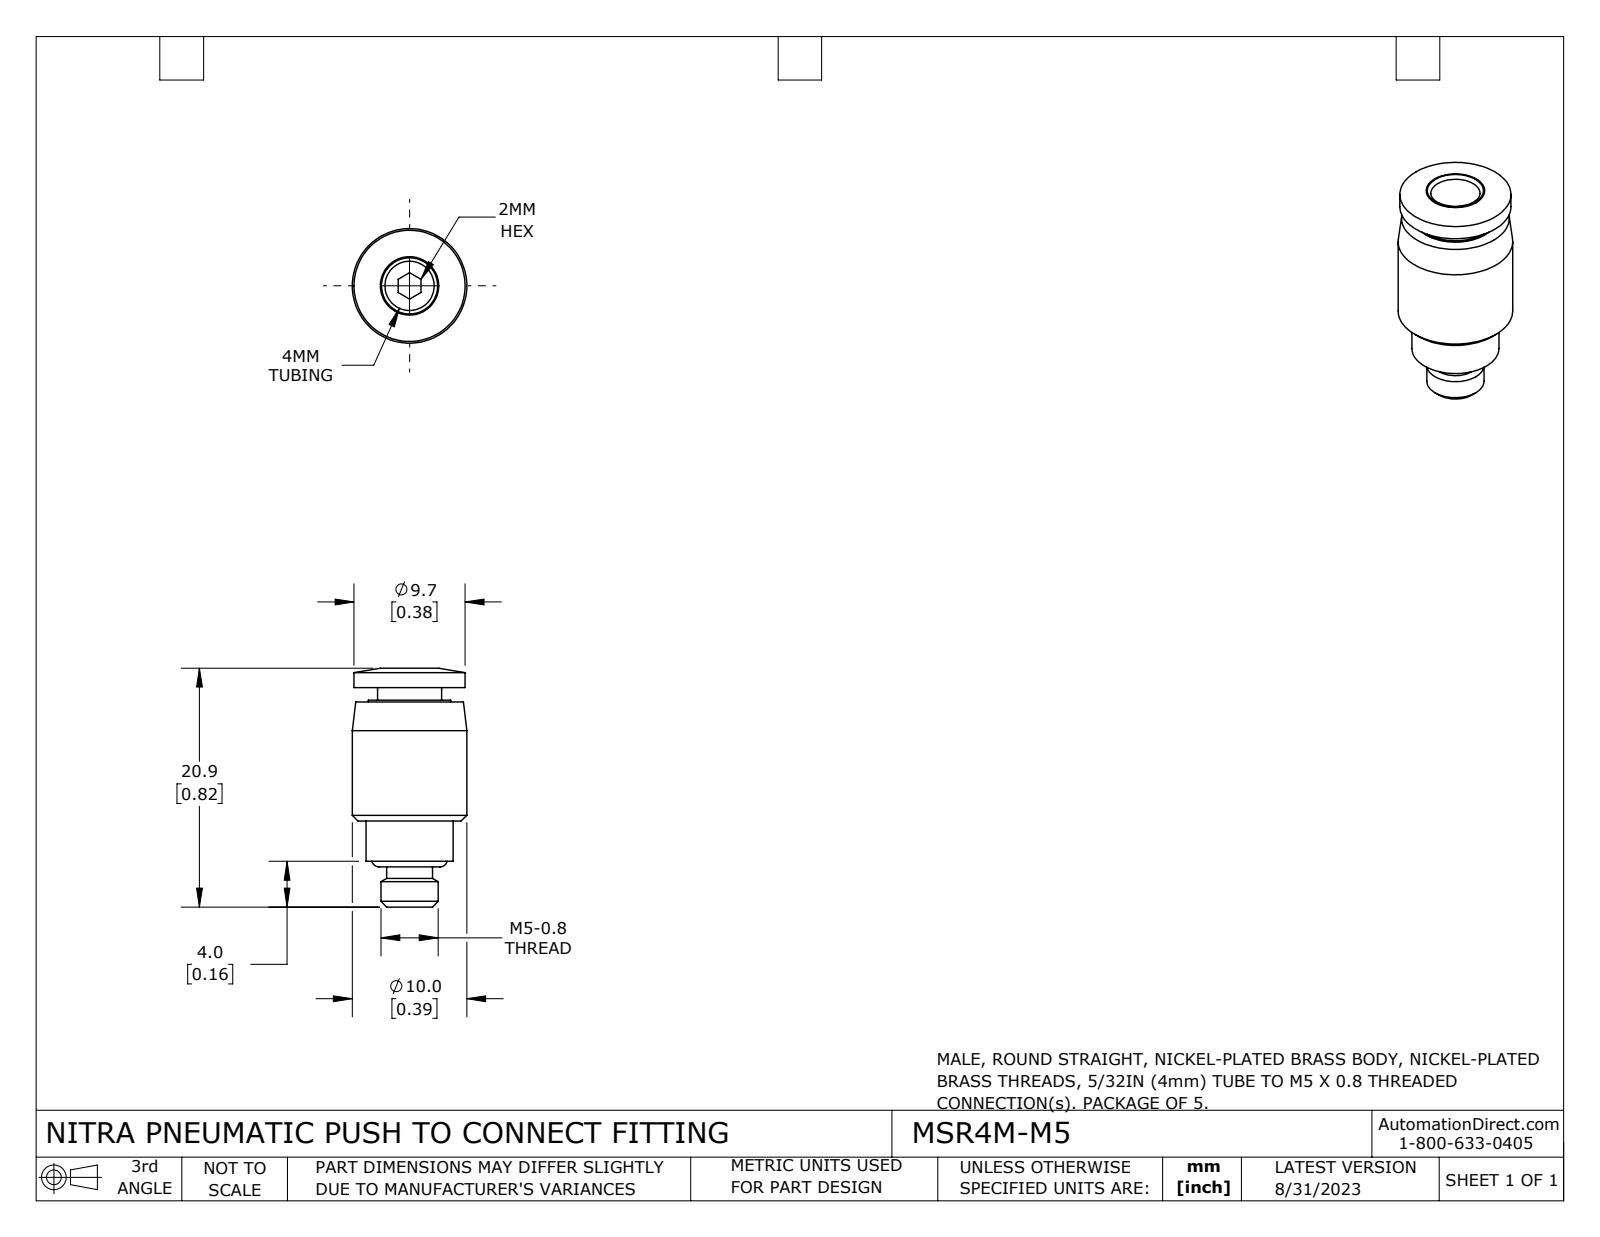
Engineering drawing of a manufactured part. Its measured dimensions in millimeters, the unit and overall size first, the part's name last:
Units: millimetres
Overall size (bounding box): 20.9 × 10 × 10
Round holes (diameter × count): ⌀2 ×1, ⌀4.3 ×1
Round bosses / shafts (diameter × count): ⌀10 ×1, ⌀9.7 ×1, ⌀7.6 ×1, ⌀7.2 ×1, ⌀5.6 ×1, ⌀5 ×1, ⌀4 ×1
Main face-to-face distances: 1.2, 1.3, 10.4, 11.7, 2.7, 13.1, 14.4, 13.3, 10.5, 1.1
Volume: 950 mm³ · Surface area: 1 089 mm²
Bodies: 2 solids, 50 faces (10 planar, 20 cylindrical, 20 other)
Part name (STEP PRODUCT): MSR4M-M5
STEP written by: SolidWorks 2015 (AUTOMOTIVE_DESIGN)
